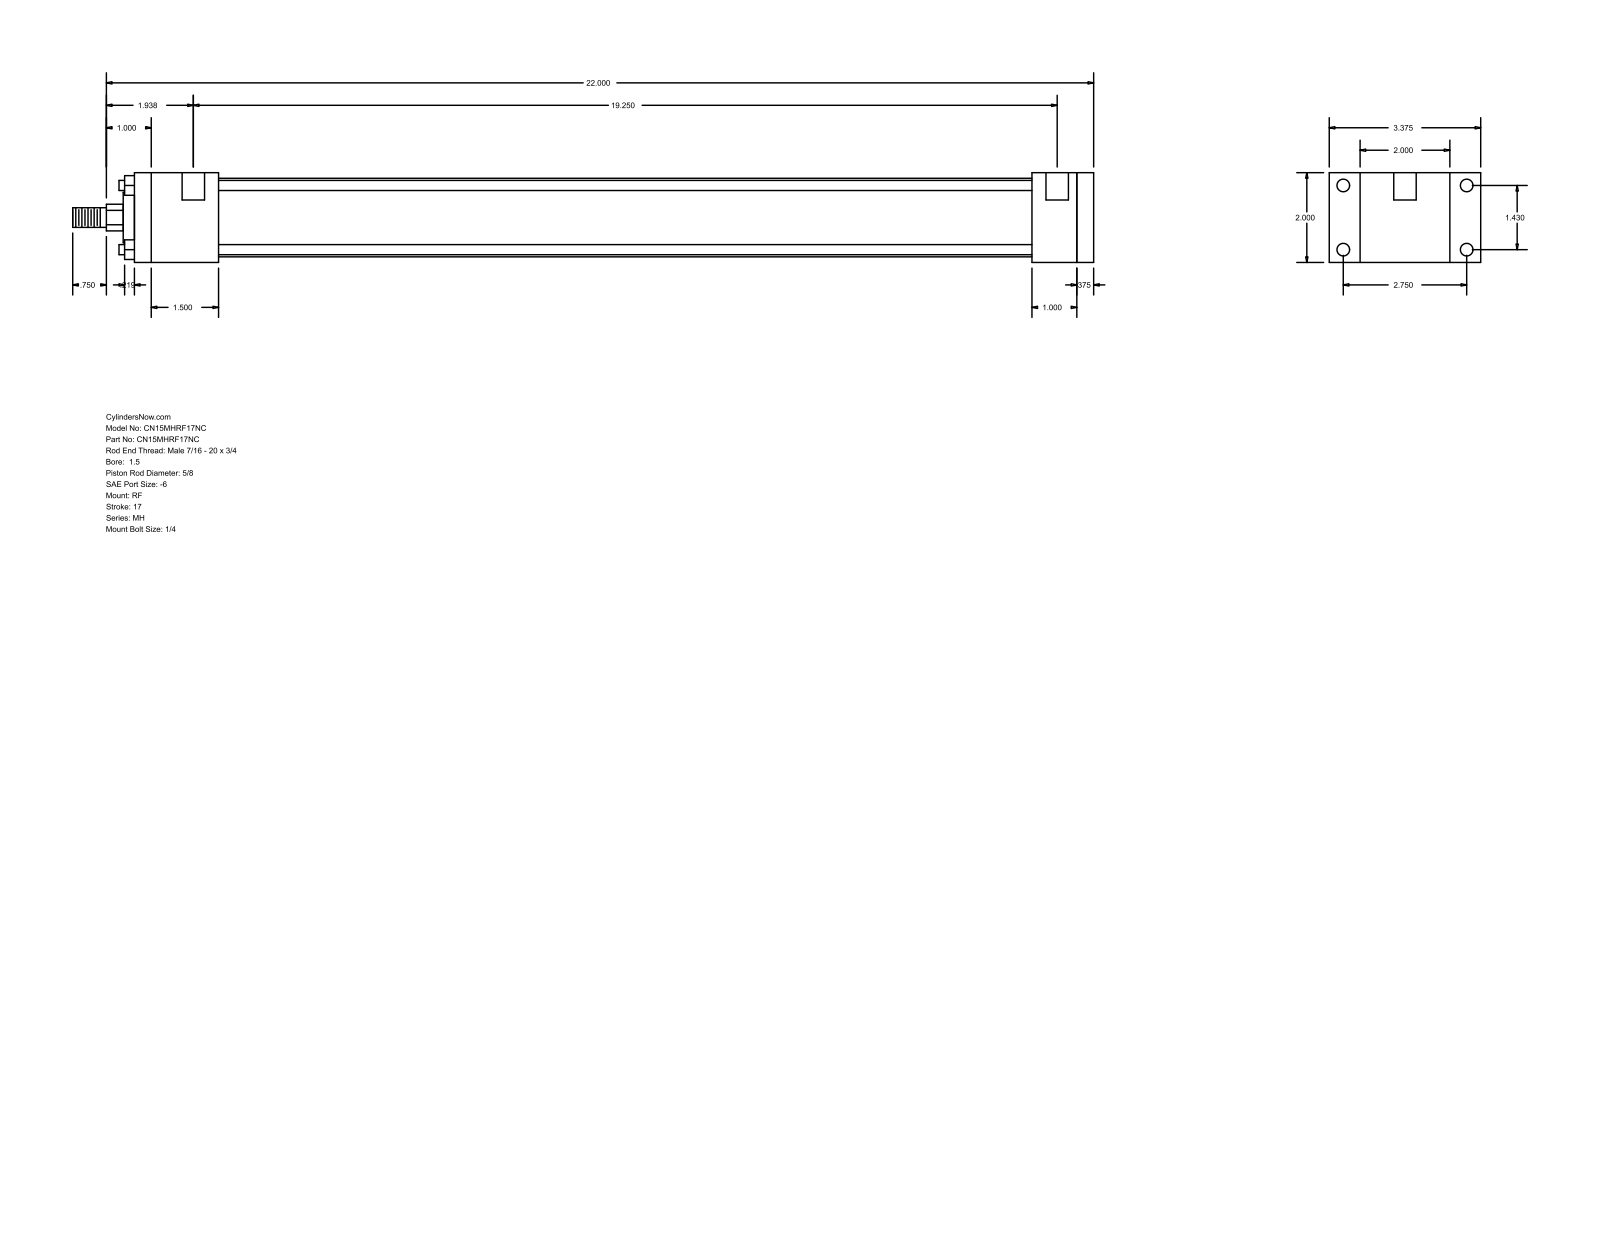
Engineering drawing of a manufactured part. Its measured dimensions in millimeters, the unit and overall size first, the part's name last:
Units: millimetres
Overall size (bounding box): 577.85 × 85.72 × 50.8
Round holes (diameter × count): ⌀5.56 ×4, ⌀7.14 ×4, ⌀12.7 ×2
Round bosses / shafts (diameter × count): ⌀5.71 ×4, ⌀44.45 ×1, ⌀28.57 ×1, ⌀15.88 ×1, ⌀11.11 ×1
Partial cylindrical surfaces — rounded edges, fillets, slot ends (radius × count): R7.54 ×1
Main face-to-face distances: 50.8, 9.53, 542.92, 533.39, 17.46, 68.26, 508, 25.39, 34.92, 47.62
Hole centre spacings: 36.32, 69.84, 78.72, 492.12, 3.17, 488.95
Bodies: 0 solids, 92 faces (64 planar, 28 cylindrical, 0 other)
Part name (STEP PRODUCT): MH_RF__0150_0.625
STEP written by: GSSL Pune (CONFIG_CONTROL_DESIGN)
